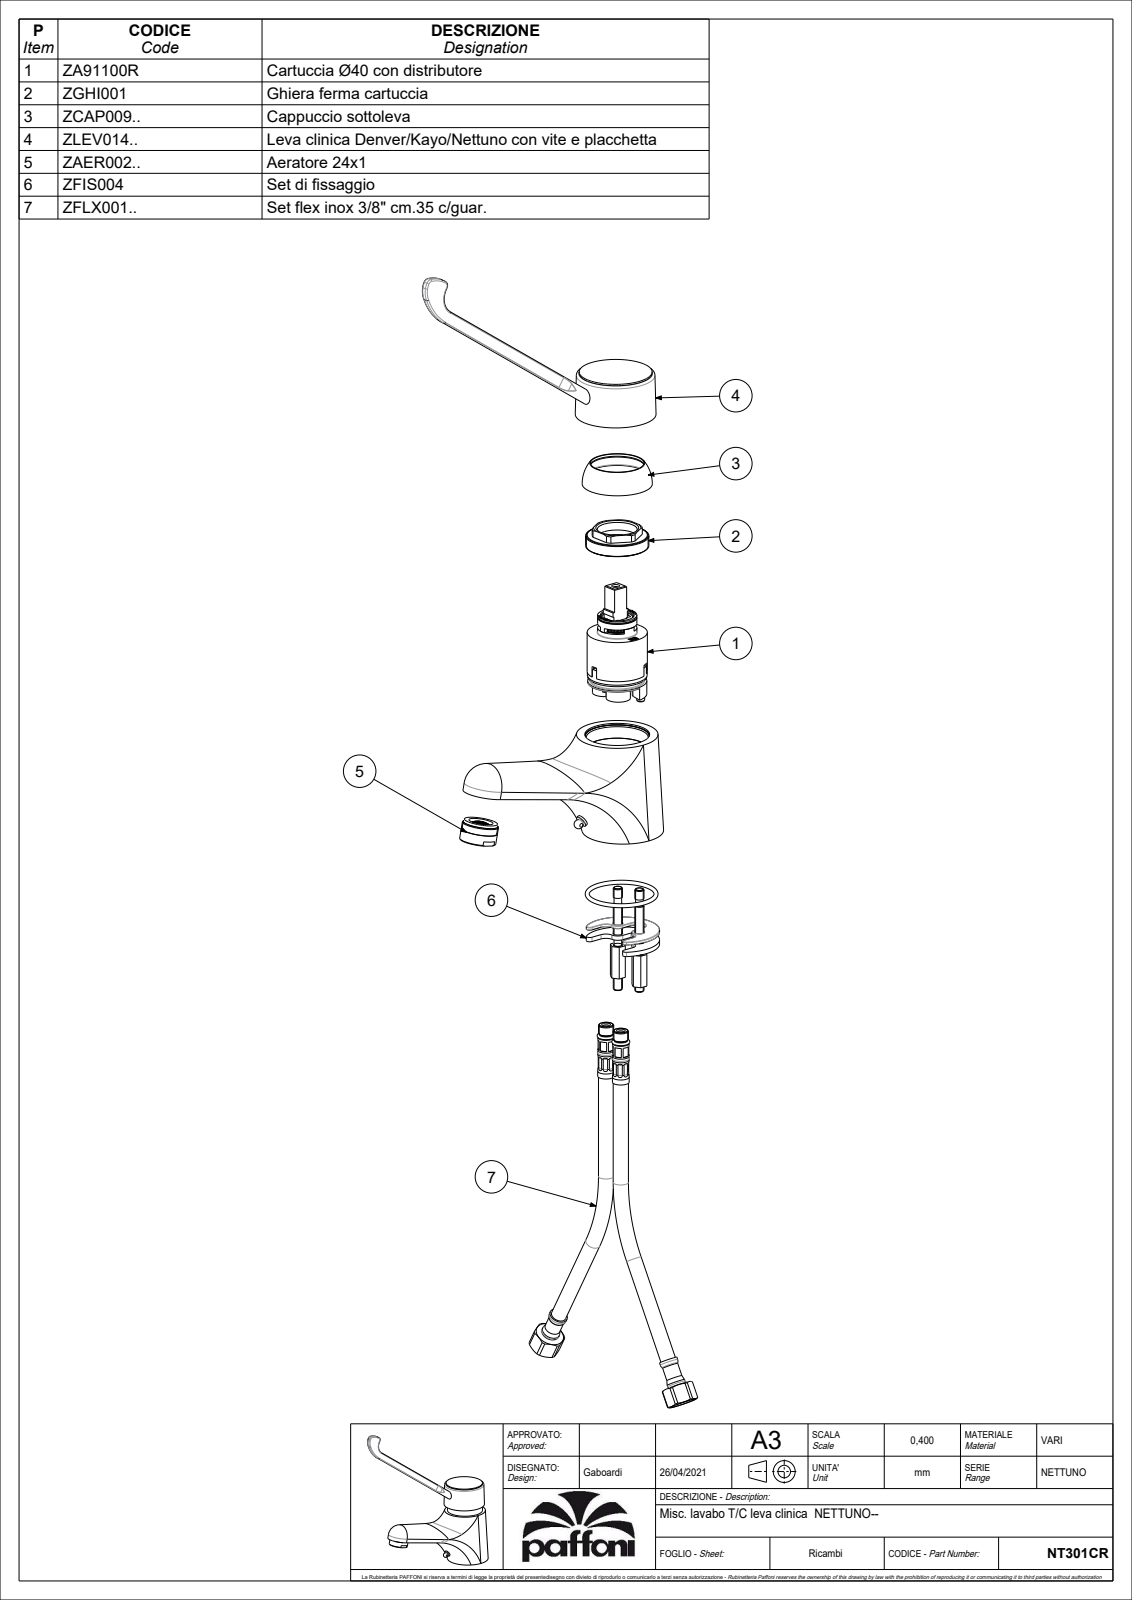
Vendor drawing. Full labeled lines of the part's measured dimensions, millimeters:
Part name (STEP PRODUCT): NT301CR
STEP written by: CREO PARAMETRIC BY PTC INC, 2020044 (CONFIG_CONTROL_DESIGN)
Units: millimetres
Bodies: 2 solids, 2832 faces (2108 planar, 408 cylindrical, 316 other)
Overall size (bounding box): 208.58 × 194.18 × 53.5
Volume: 156 486 mm³ · Surface area: 100 318 mm²
Round holes (diameter × count): ⌀8 ×4, ⌀11 ×3, ⌀5.5 ×2, ⌀7 ×2, ⌀9 ×2, ⌀12 ×2, ⌀21 ×2, ⌀2.5 ×1, ⌀3.3 ×1, ⌀4 ×1, ⌀4.3 ×1, ⌀5 ×1
Round bosses / shafts (diameter × count): ⌀15.9 ×2, ⌀10 ×2, ⌀9.4 ×2, ⌀47.85 ×1, ⌀41.7 ×1, ⌀39.5 ×1, ⌀39.2 ×1, ⌀38.8 ×1
Partial cylindrical surfaces — rounded edges, fillets, slot ends (radius × count): R0.5 ×69, R0.2 ×24, R0.3 ×8, R1.5 ×6, R7.5 ×4, R2 ×2, R5.5 ×2, R6.5 ×2
Main face-to-face distances: 3.5, 6, 4.5, 1.5, 3, 0.5, 4, 10, 22, 38.1
Hole centre spacings: 1.12, 9.9, 13.04, 14.53, 2, 8.6, 9.6, 10.97
